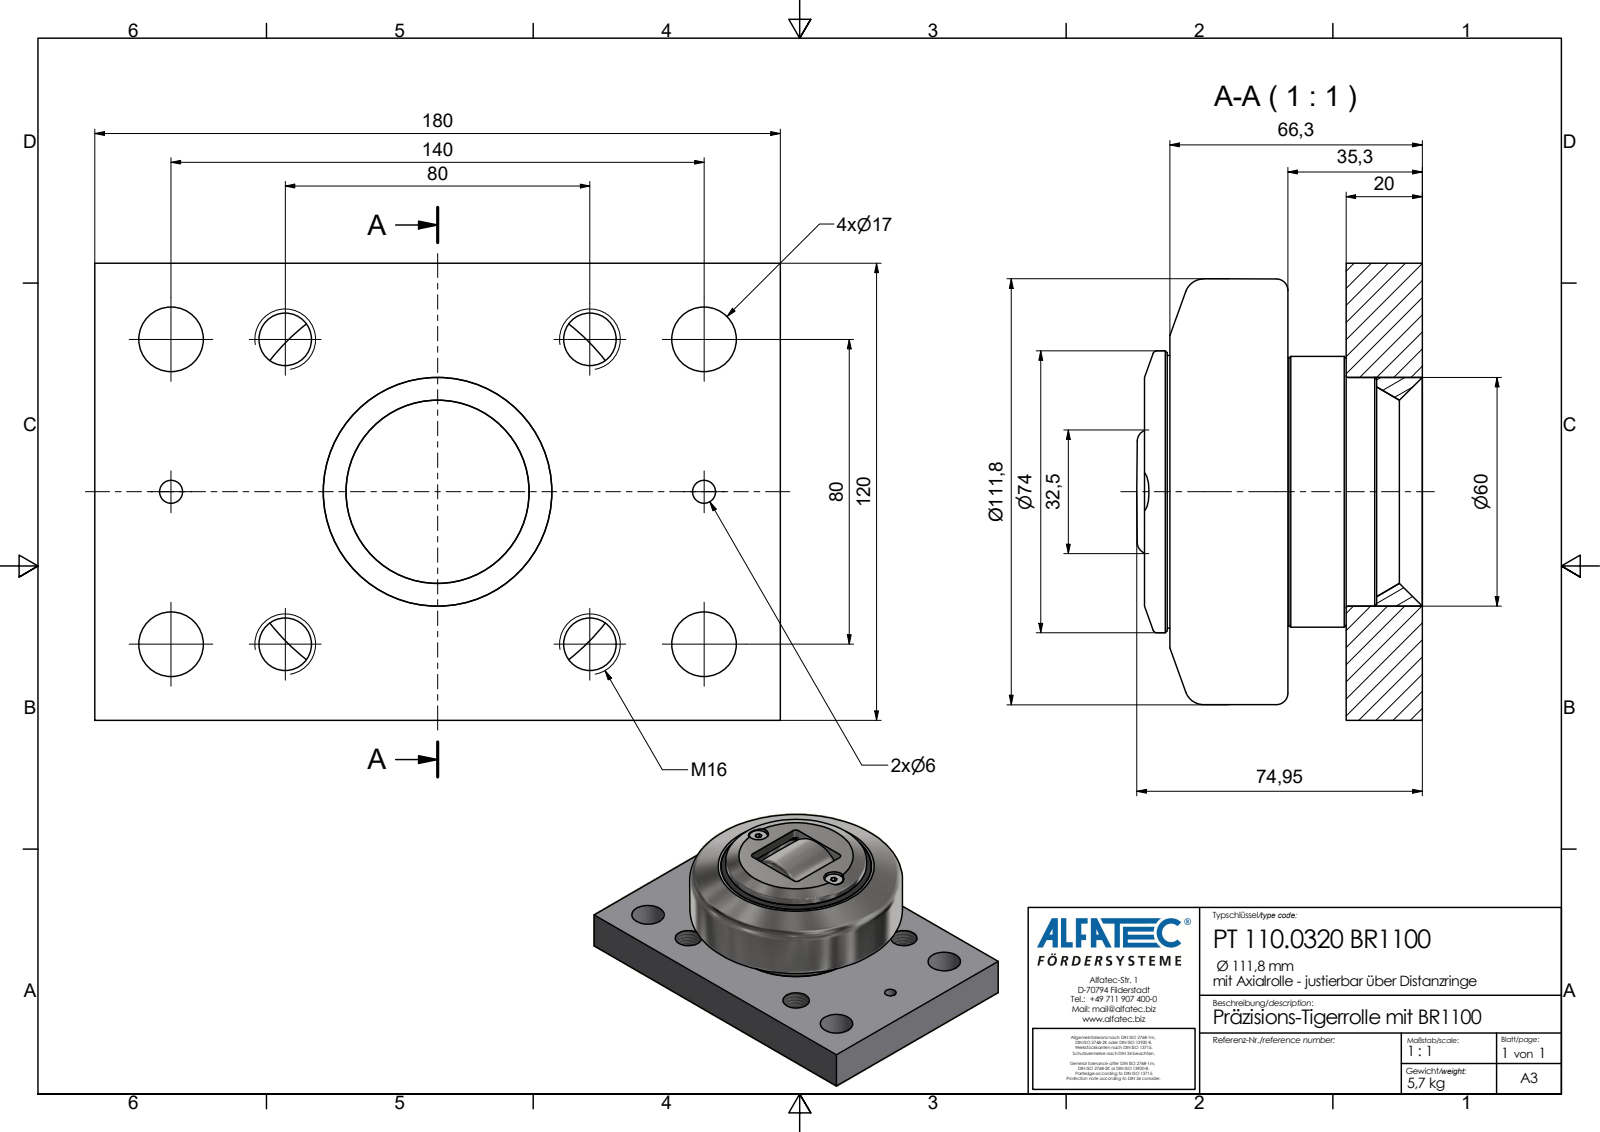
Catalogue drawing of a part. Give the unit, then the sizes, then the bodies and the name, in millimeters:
Units: millimetres
Overall size (bounding box): 180 × 120 × 74.95
Round holes (diameter × count): ⌀13.84 ×4, ⌀17 ×4, ⌀6 ×2, ⌀10.5 ×2
Round bosses / shafts (diameter × count): ⌀9.75 ×2, ⌀74 ×1, ⌀71.6 ×1, ⌀71 ×1, ⌀70.5 ×1
Partial cylindrical surfaces — rounded edges, fillets, slot ends (radius × count): R2 ×4, R11.5 ×1, R14 ×1, R24 ×1
Main face-to-face distances: 20, 35.3, 15.3, 120, 180, 72.95, 52.95, 37.65, 66.3, 46.3
Hole centre spacings: 80, 30, 40, 41.76, 50, 58, 78.89, 85.44
Volume: 775 444 mm³ · Surface area: 87 642 mm²
Bodies: 1 solid, 88 faces (40 planar, 30 cylindrical, 18 other)
Part name (STEP PRODUCT): PT 110.0320 BR1100_Kontur
STEP written by: Autodesk Inventor 2020 (AP242_MANAGED_MODEL_BASED_3D_ENGINEERING_MIM_LF)
